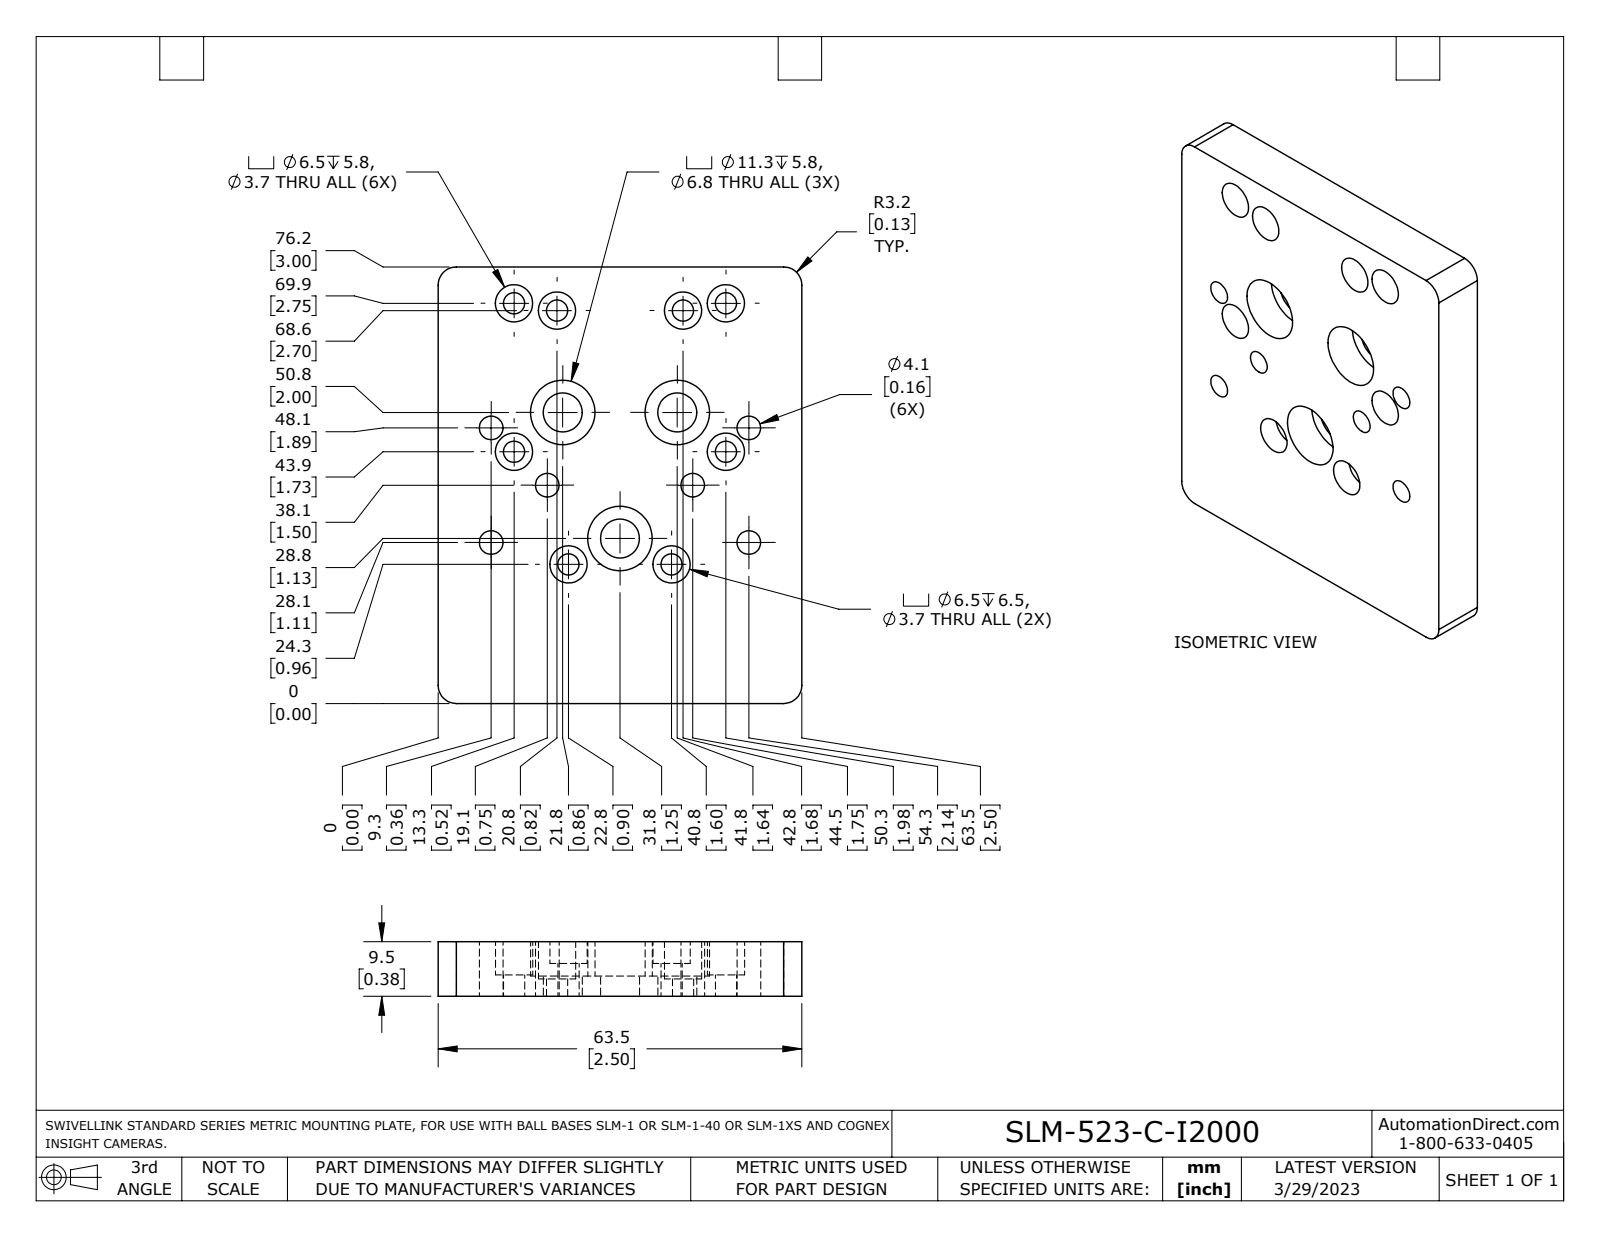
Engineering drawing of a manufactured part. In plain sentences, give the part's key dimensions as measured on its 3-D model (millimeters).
The part is named "SLM-523-C-I2000". Its 3-D file was written by "SolidWorks 2021 (AUTOMOTIVE_DESIGN)". It is 1 solid with 49 faces: 17 planar, 32 cylindrical and 0 other. Overall it measures 76.2 by 63.5 by 9.5 millimeters. Its volume is 41 260 cubic millimeters and its surface area 14 590 square millimeters. Round holes: 8 of diameter 3.7, 8 of diameter 6.5, 6 of diameter 4.1, 3 of diameter 6.8, 3 of diameter 11.3. Partial cylindrical surfaces (rounded edges, fillets, slot ends): 4 of radius 3.2. The main face-to-face distances are 9.5, 63.5, 76.2, 3.5, 6, 3.7, 5.8, 5.7, 2.2, 2. The hole center spacings are 14, 25.9, 36.6, 20, 5.8, 7.6, 8.2, 10.1.
